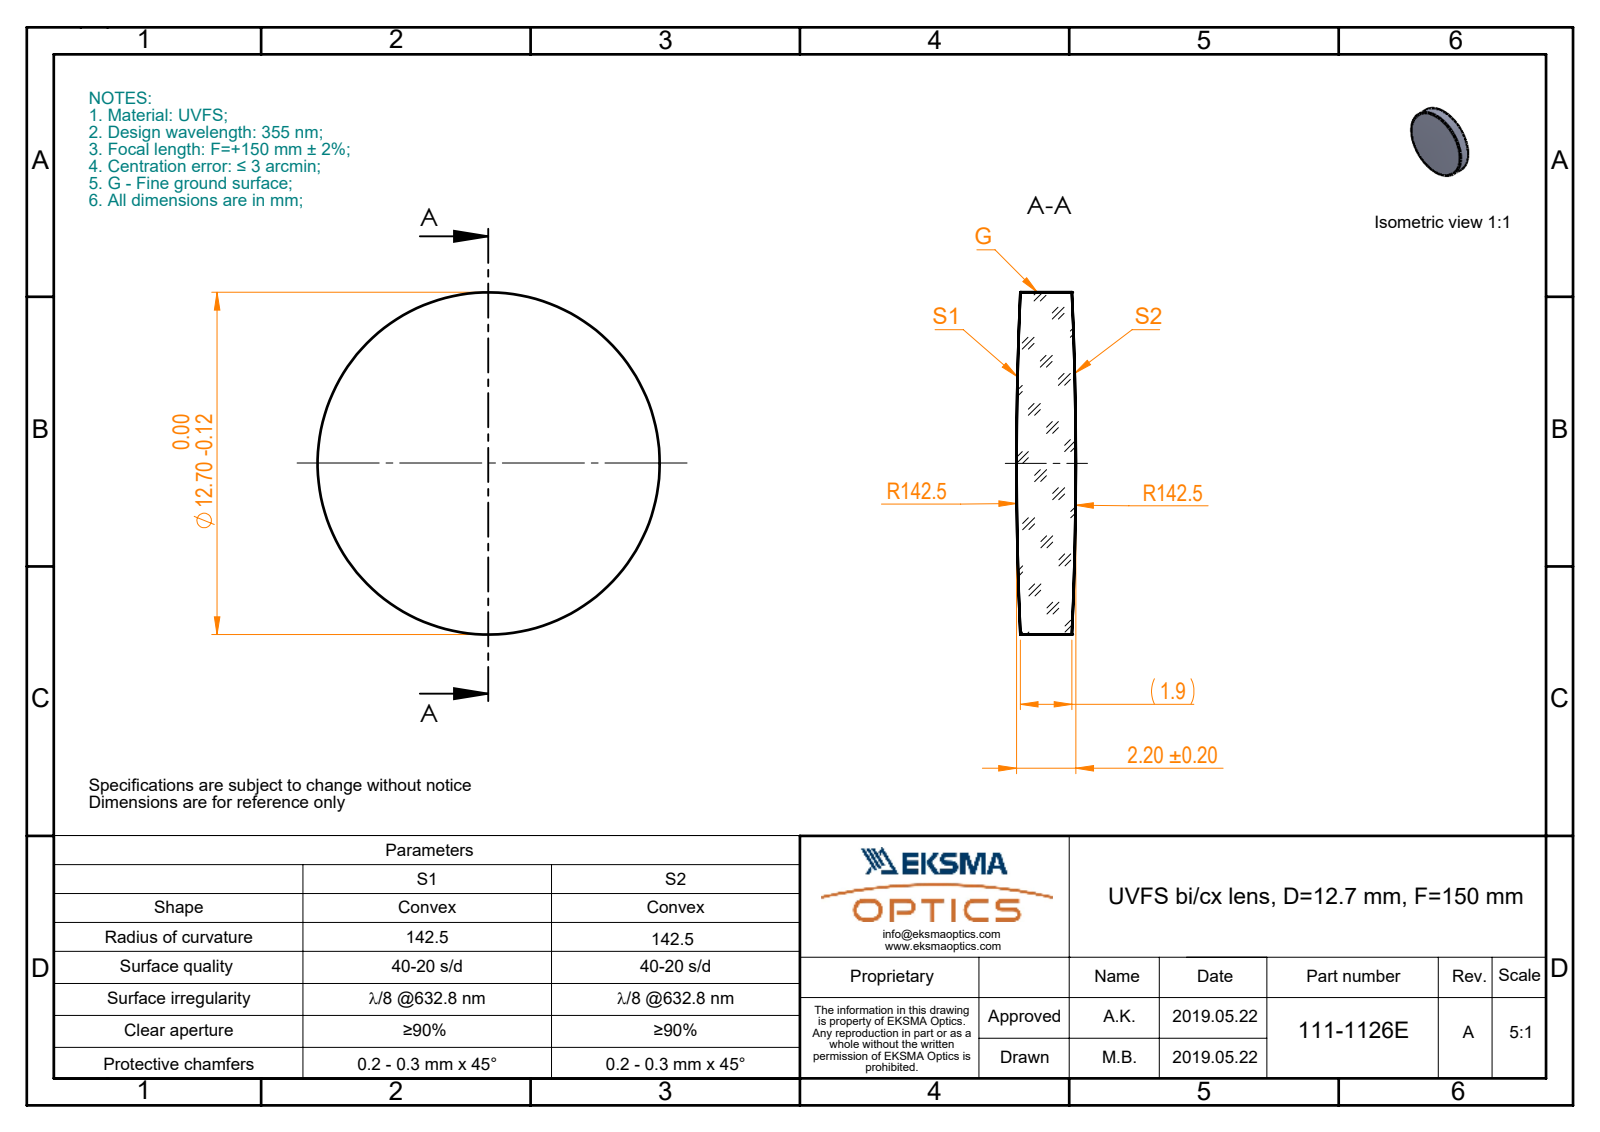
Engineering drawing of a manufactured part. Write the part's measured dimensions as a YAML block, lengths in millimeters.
part_name: "111-1126E UVFS bi-cx 12.7 F150"
step_written_by: "SolidWorks 2017 (CONFIG_CONTROL_DESIGN)"
units: millimeters
bodies: {solids: 1, faces: 6, planar: 0, cylindrical: 2, other: 4}
overall_size: [12.7, 12.7, 2.2]
volume: 261
surface_area: 330
round_bosses_or_shafts:
  - {diameter: 12.7, count: 1}
